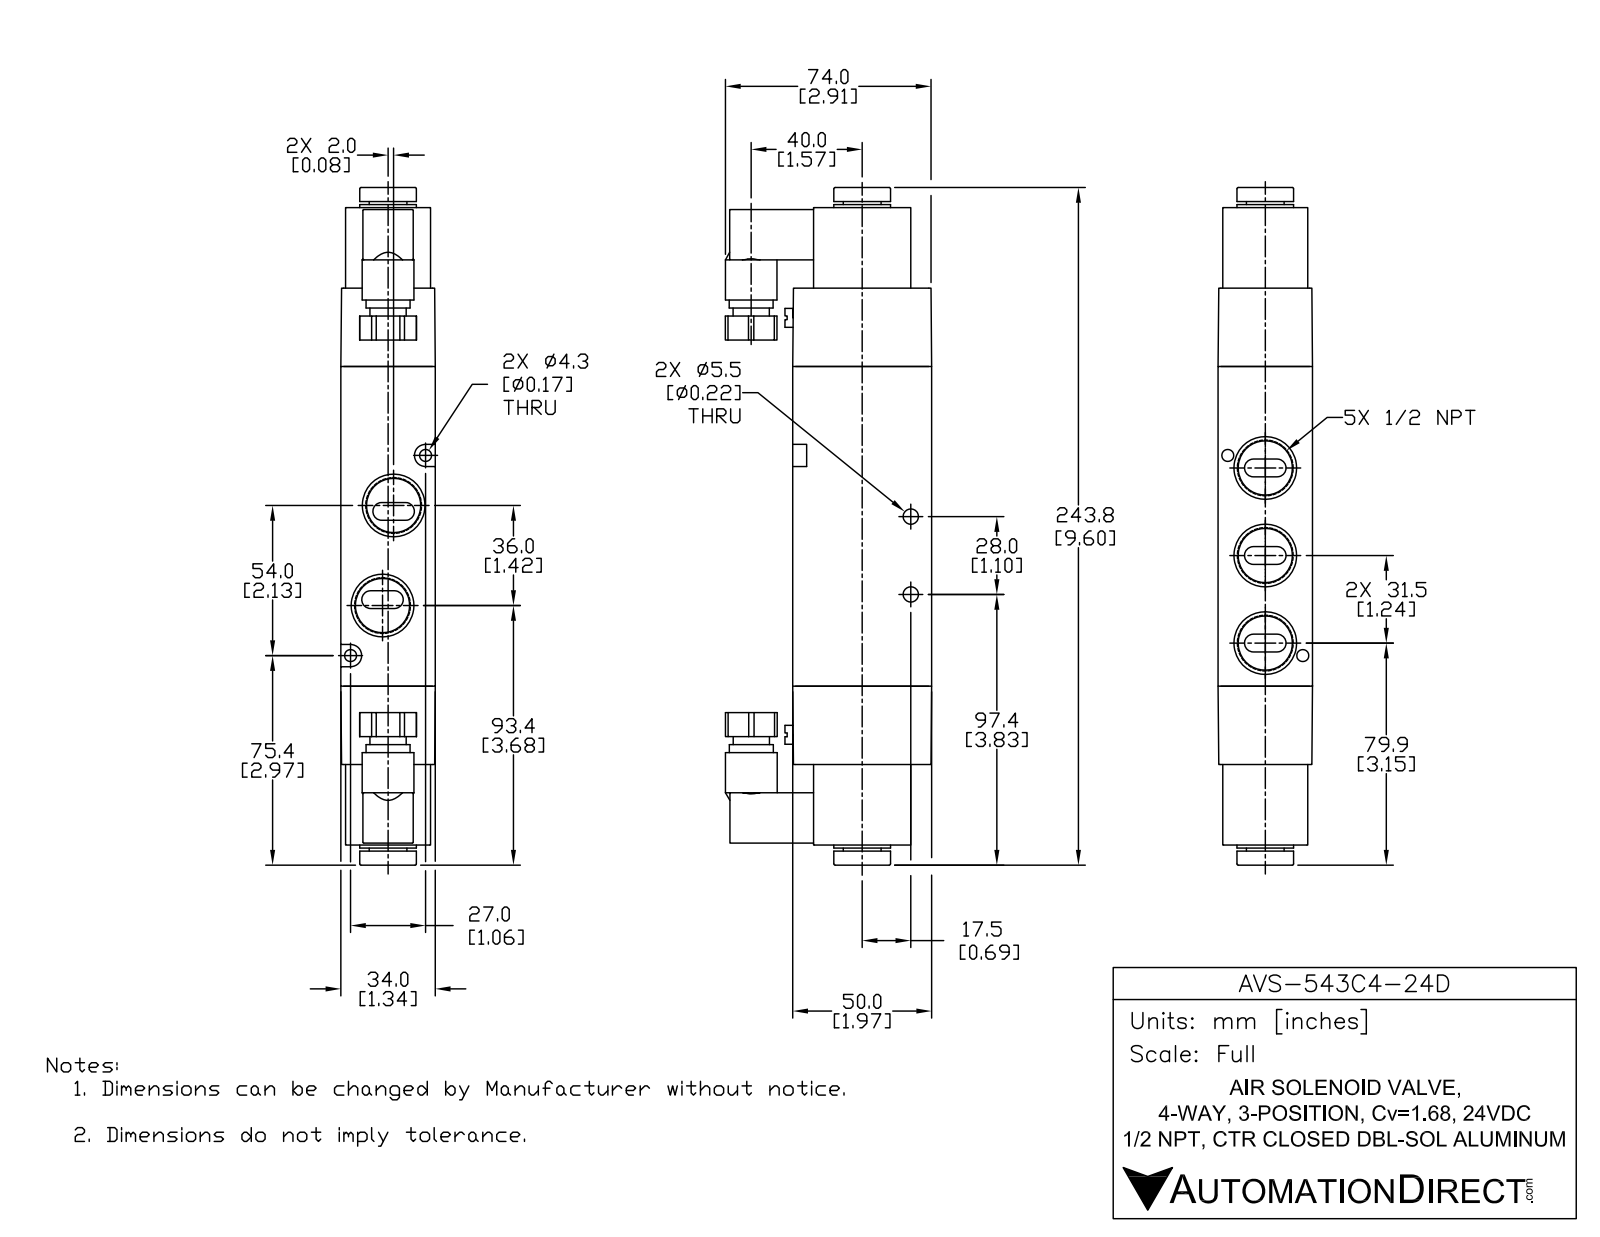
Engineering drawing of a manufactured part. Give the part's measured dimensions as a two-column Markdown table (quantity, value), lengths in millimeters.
| quantity | value |
| --- | --- |
| part name | AVS-543C4-24D |
| STEP written by | SolidWorks 2015 (CONFIG_CONTROL_DESIGN) |
| units | millimeters |
| bodies | 5 solids, 248 faces (111 planar, 103 cylindrical, 34 other) |
| overall size | 243.8 × 74.2 × 34 |
| volume | 356 277 mm³ |
| surface area | 64 523 mm² |
| round holes (diameter × count) | 17.86 × 5, 4.3 × 2, 5.5 × 2, 9.3 × 1 |
| round bosses / shafts (diameter × count) | 6.7 × 2, 20.8 × 1, 20.4 × 1, 18.6 × 1, 15.8 × 1, 13.6 × 1, 13 × 1 |
| partial cylindrical surfaces (radius × count) | 1.5 × 18, 1 × 10, 3.2 × 10, 4 × 2 |
| main face-to-face distances | 34, 115, 50, 35.96, 28.2, 32.14, 51.96, 7.95, 26.05, 18.1 |
| hole center spacings | 13.65, 14.23, 18.11, 21.36, 31.5, 38.45, 49.54, 56.18 |
